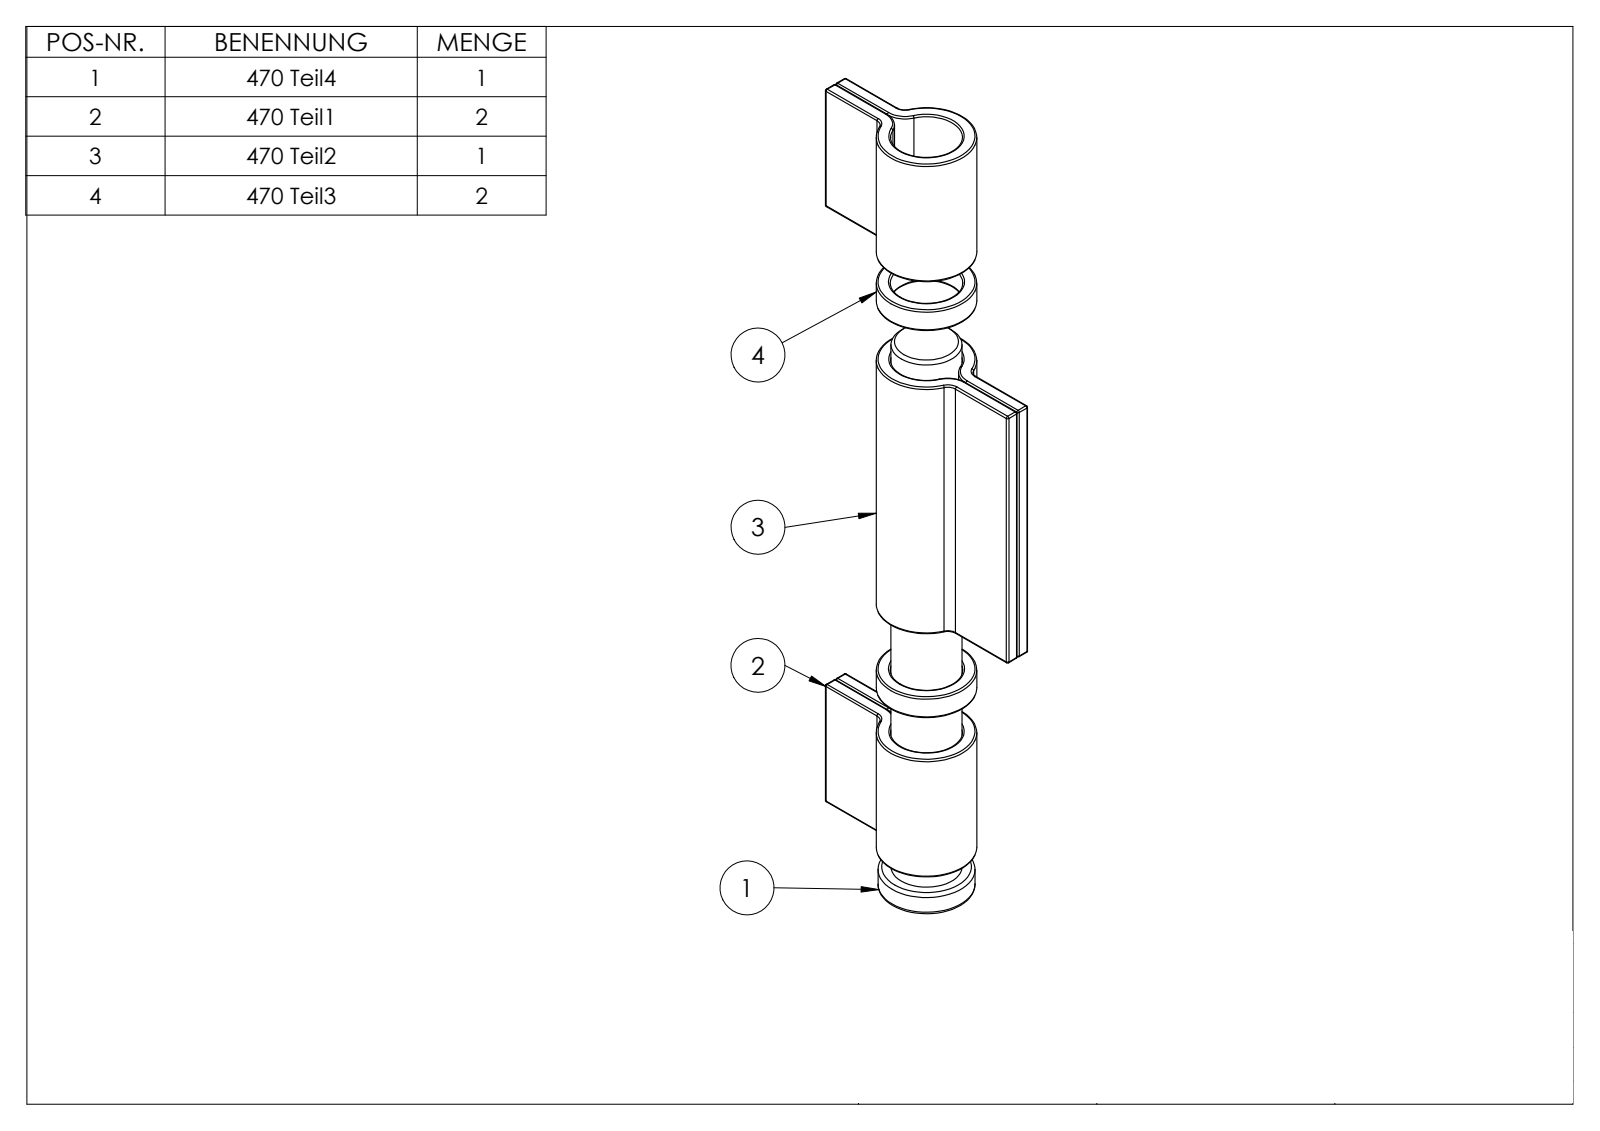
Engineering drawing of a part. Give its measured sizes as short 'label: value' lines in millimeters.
name: 470 Teil1; 470 Teil4; 470 Teil3; 470 (+1 more)
written by: SolidWorks 2018 (CONFIG_CONTROL_DESIGN)
unit: mm
bodies: 6 solids, 320 faces (104 planar, 88 cylindrical, 128 other)
size: 186 × 72 × 28
volume: 140 210 mm³; area: 58 202 mm²
holes: 1× ⌀20, 1× ⌀20.2
bosses: 1× ⌀28, 1× ⌀27, 1× ⌀19.8
rounds: 38× R0.5, 4× R3, 4× R7
face distances: 4, 4.1, 8.1, 7, 47, 138, 91, 40, 131, 98
